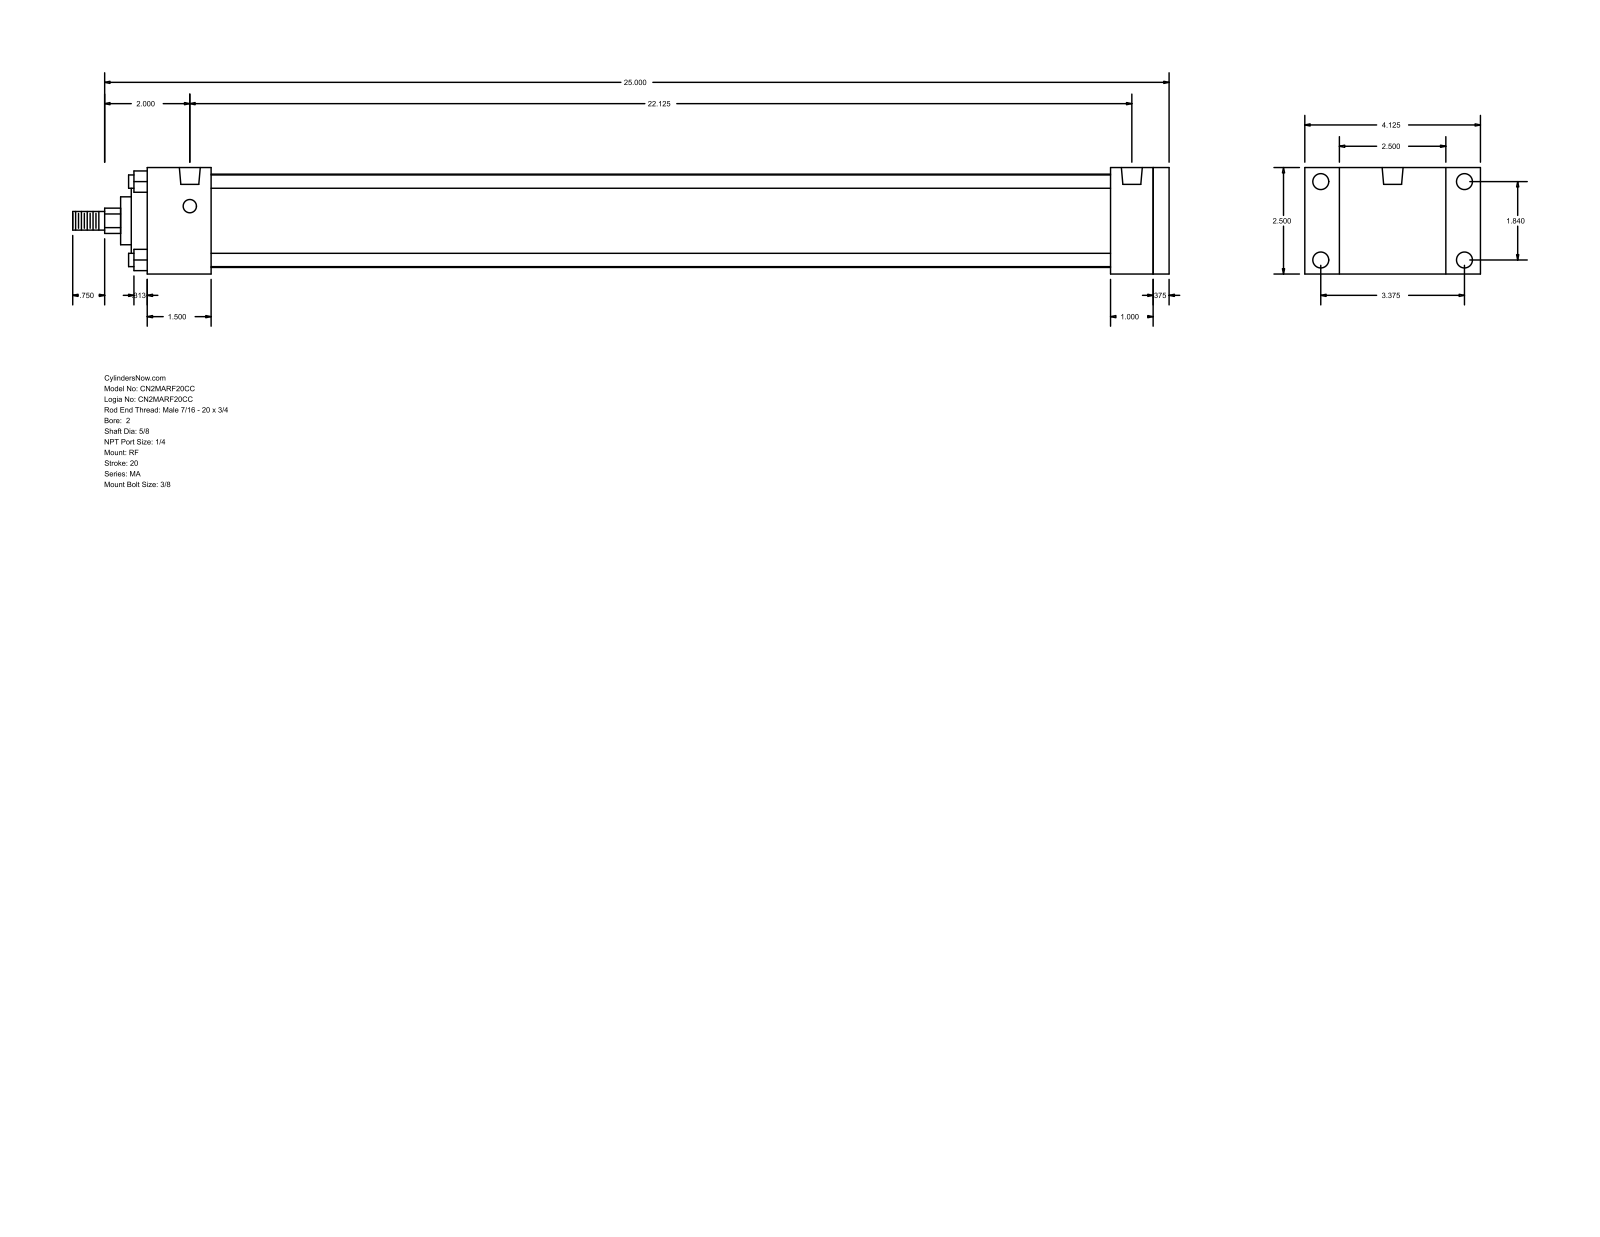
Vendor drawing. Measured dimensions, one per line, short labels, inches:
name: MA_RF__0200_0.625
written by: GSSL Pune (CONFIG_CONTROL_DESIGN)
unit: in
bodies: 0 solids, 94 faces (65 planar, 29 cylindrical, 0 other)
size: 25.75 × 4.125 × 2.5
holes: 4× ⌀0.313, 4× ⌀0.375, 2× ⌀0.492
bosses: 4× ⌀0.313, 1× ⌀2.19, 1× ⌀2, 1× ⌀1.125, 1× ⌀0.625, 1× ⌀0.437
rounds: 1× R0.297
face distances: 2.5, 0.375, 24, 1, 1.5, 23.625, 22.125, 22.5, 22.625, 21.125
hole spacings: 1.84, 3.375, 3.844, 22.125
